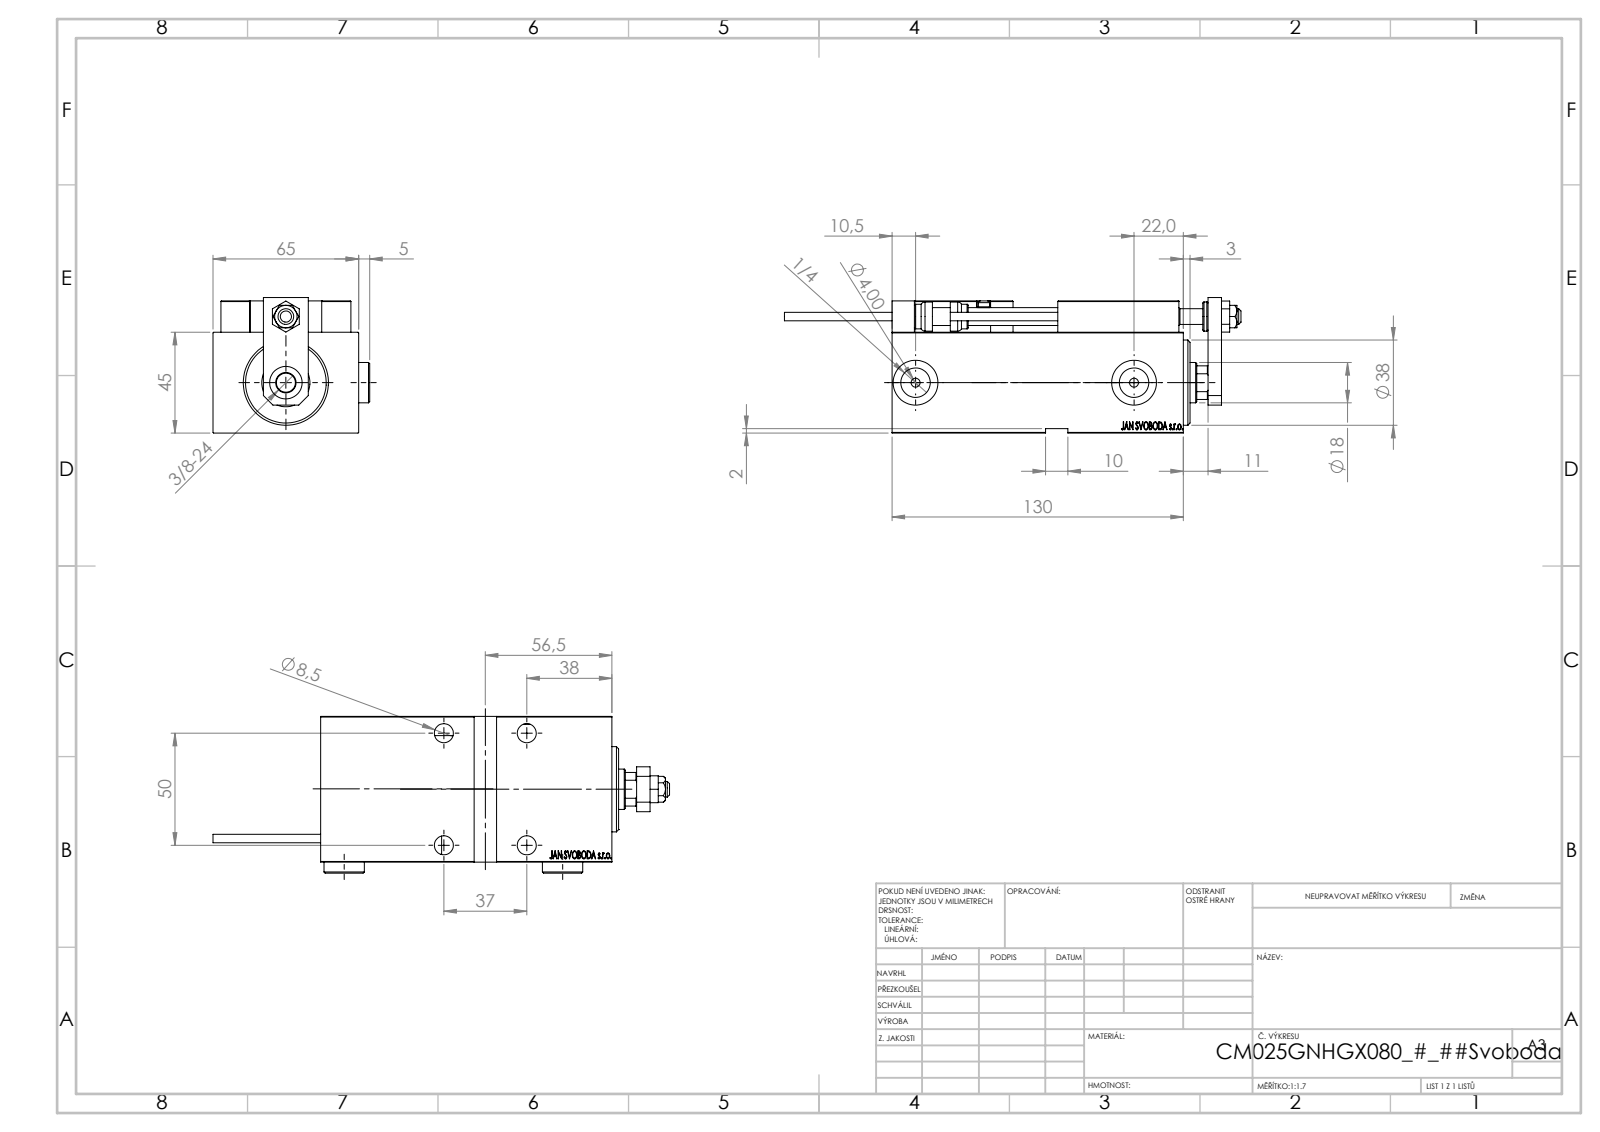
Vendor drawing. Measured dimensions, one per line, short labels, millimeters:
name: NUT_D12; ALLEN BOLT D8; KONCOVKA; TYC_L79 (+8 more)
written by: SolidWorks 2019 (CONFIG_CONTROL_DESIGN)
unit: mm
bodies: 26 solids, 1334 faces (601 planar, 188 cylindrical, 545 other)
size: 203.7 × 69.9 × 60.5
volume: 396 448 mm³; area: 91 013 mm²
holes: 6× ⌀4, 5× ⌀8, 5× ⌀8.5, 4× ⌀3.2, 4× ⌀13.5, 2× ⌀5, 2× ⌀13.16, 2× ⌀20, 1× ⌀7, 1× ⌀14.5, 1× ⌀18, 1× ⌀21.5
bosses: 2× ⌀18, 2× ⌀5, 2× ⌀3.8, 1× ⌀38, 1× ⌀13, 1× ⌀11
rounds: 30× R0.3, 2× R3, 1× R8.5
face distances: 45, 65, 14, 6, 59, 130, 13, 141, 5, 19
hole spacings: 11.37, 20, 29.59, 29.69, 34.44, 36.06, 37, 42.19
